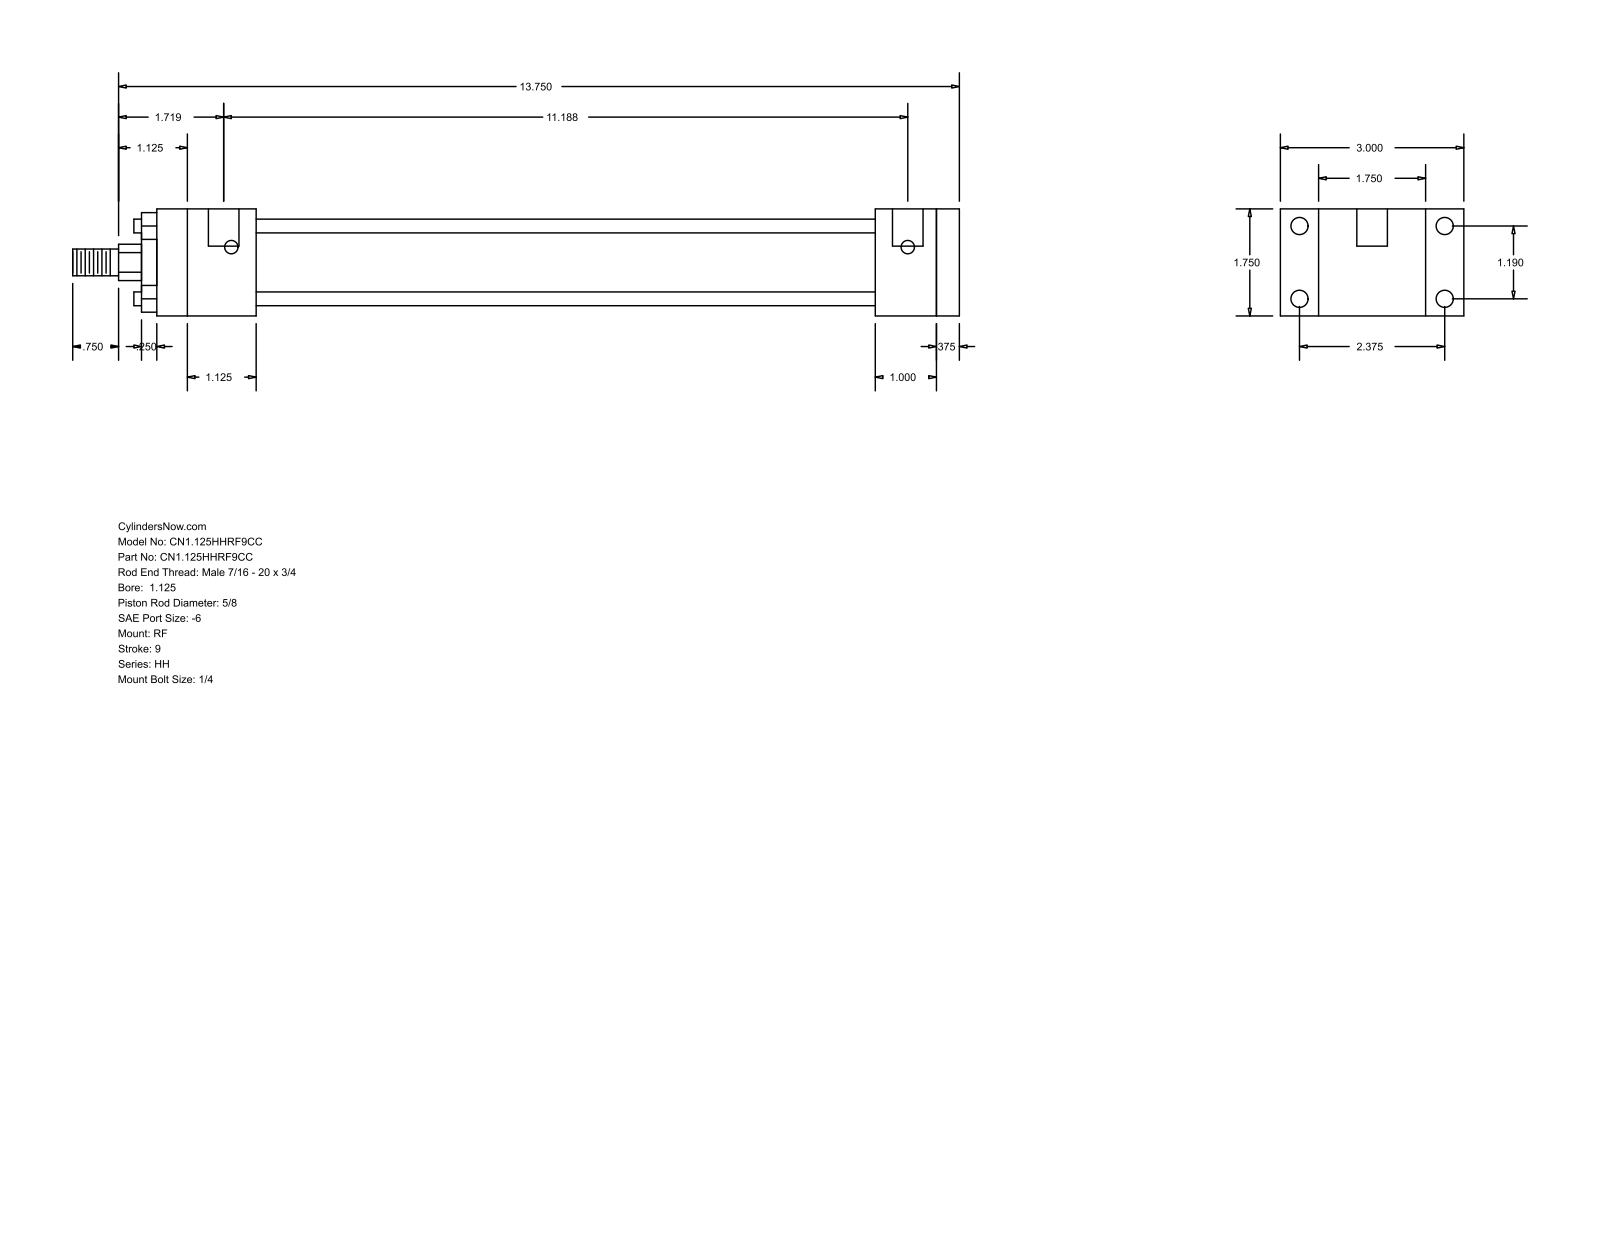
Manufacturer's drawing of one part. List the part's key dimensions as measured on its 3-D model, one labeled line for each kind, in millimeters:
Part name (STEP PRODUCT): HH_RF__0112_0.625
STEP written by: GSSL Pune (CONFIG_CONTROL_DESIGN)
Units: millimetres
Bodies: 0 solids, 92 faces (64 planar, 28 cylindrical, 0 other)
Overall size (bounding box): 368.3 × 76.2 × 44.45
Round holes (diameter × count): ⌀5.56 ×4, ⌀7.14 ×4, ⌀12.7 ×2
Round bosses / shafts (diameter × count): ⌀5.71 ×4, ⌀34.92 ×1, ⌀28.57 ×1, ⌀15.88 ×1, ⌀11.11 ×1
Partial cylindrical surfaces — rounded edges, fillets, slot ends (radius × count): R7.54 ×1
Main face-to-face distances: 44.46, 9.52, 34.93, 333.37, 15.87, 282.58, 292.1, 257.17, 25.41, 41.27
Hole centre spacings: 30.22, 60.32, 67.47, 280.99, 3.17, 284.16
